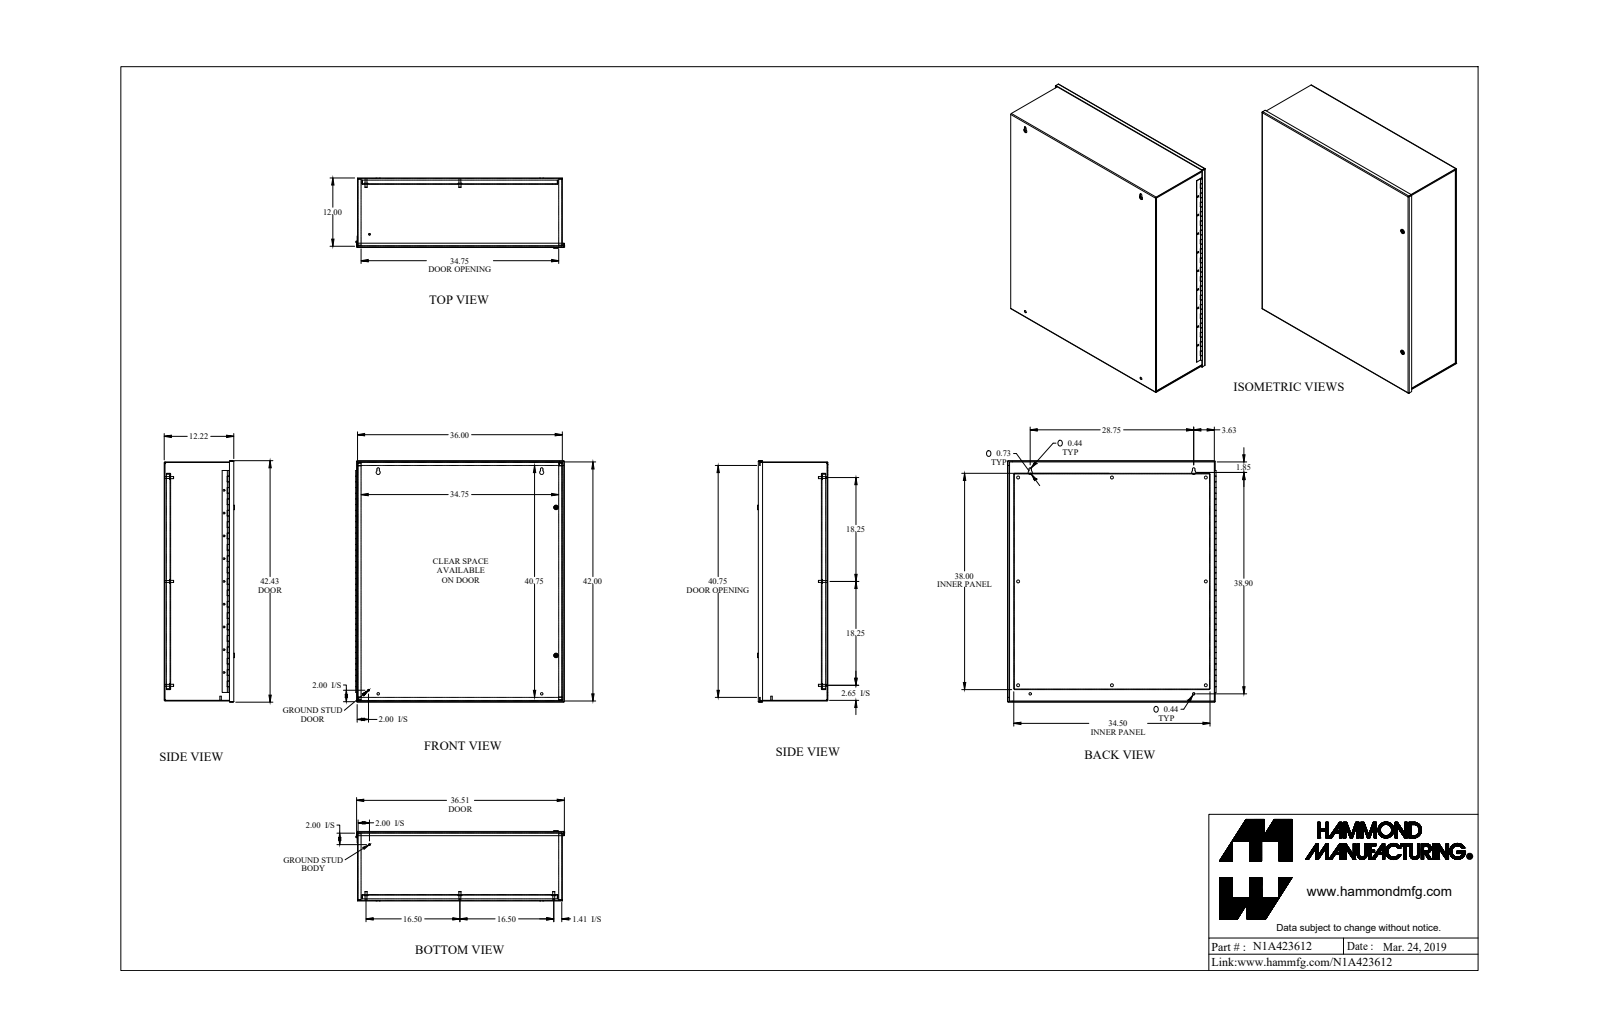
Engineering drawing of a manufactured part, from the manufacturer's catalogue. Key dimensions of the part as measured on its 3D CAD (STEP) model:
Part name (STEP PRODUCT): N1A423612
STEP written by: SolidWorks 2018 (AUTOMOTIVE_DESIGN)
Units: inches
Bodies: 31 solids, 951 faces (503 planar, 380 cylindrical, 68 other)
Overall size (bounding box): 42.43 × 36.668 × 12.342
Volume: 630.6 in³ · Surface area: 13 416 in²
Round holes (diameter × count): ⌀0.304 ×9, ⌀0.5 ×8, ⌀0.307 ×4, ⌀0.445 ×4, ⌀0.734 ×3, ⌀0.437 ×2, ⌀0.516 ×2, ⌀0.188 ×1
Round bosses / shafts (diameter × count): ⌀0.65 ×8, ⌀0.375 ×8, ⌀0.33 ×8, ⌀1 ×4, ⌀0.788 ×2, ⌀0.535 ×2, ⌀0.496 ×2, ⌀0.281 ×2
Partial cylindrical surfaces — rounded edges, fillets, slot ends (radius × count): R0.048 ×16, R0.143 ×16, R0.125 ×6, R0.03 ×5, R0.219 ×3, R0.06 ×2, R0.153 ×2, R0.315 ×2
Main face-to-face distances: 0.095, 1.032, 0.095, 12.03, 12.125, 12.125, 12.22, 11.093, 1.127, 10.998
Hole centre spacings: 4, 8, 12, 16, 20, 40.054, 24, 24.602
